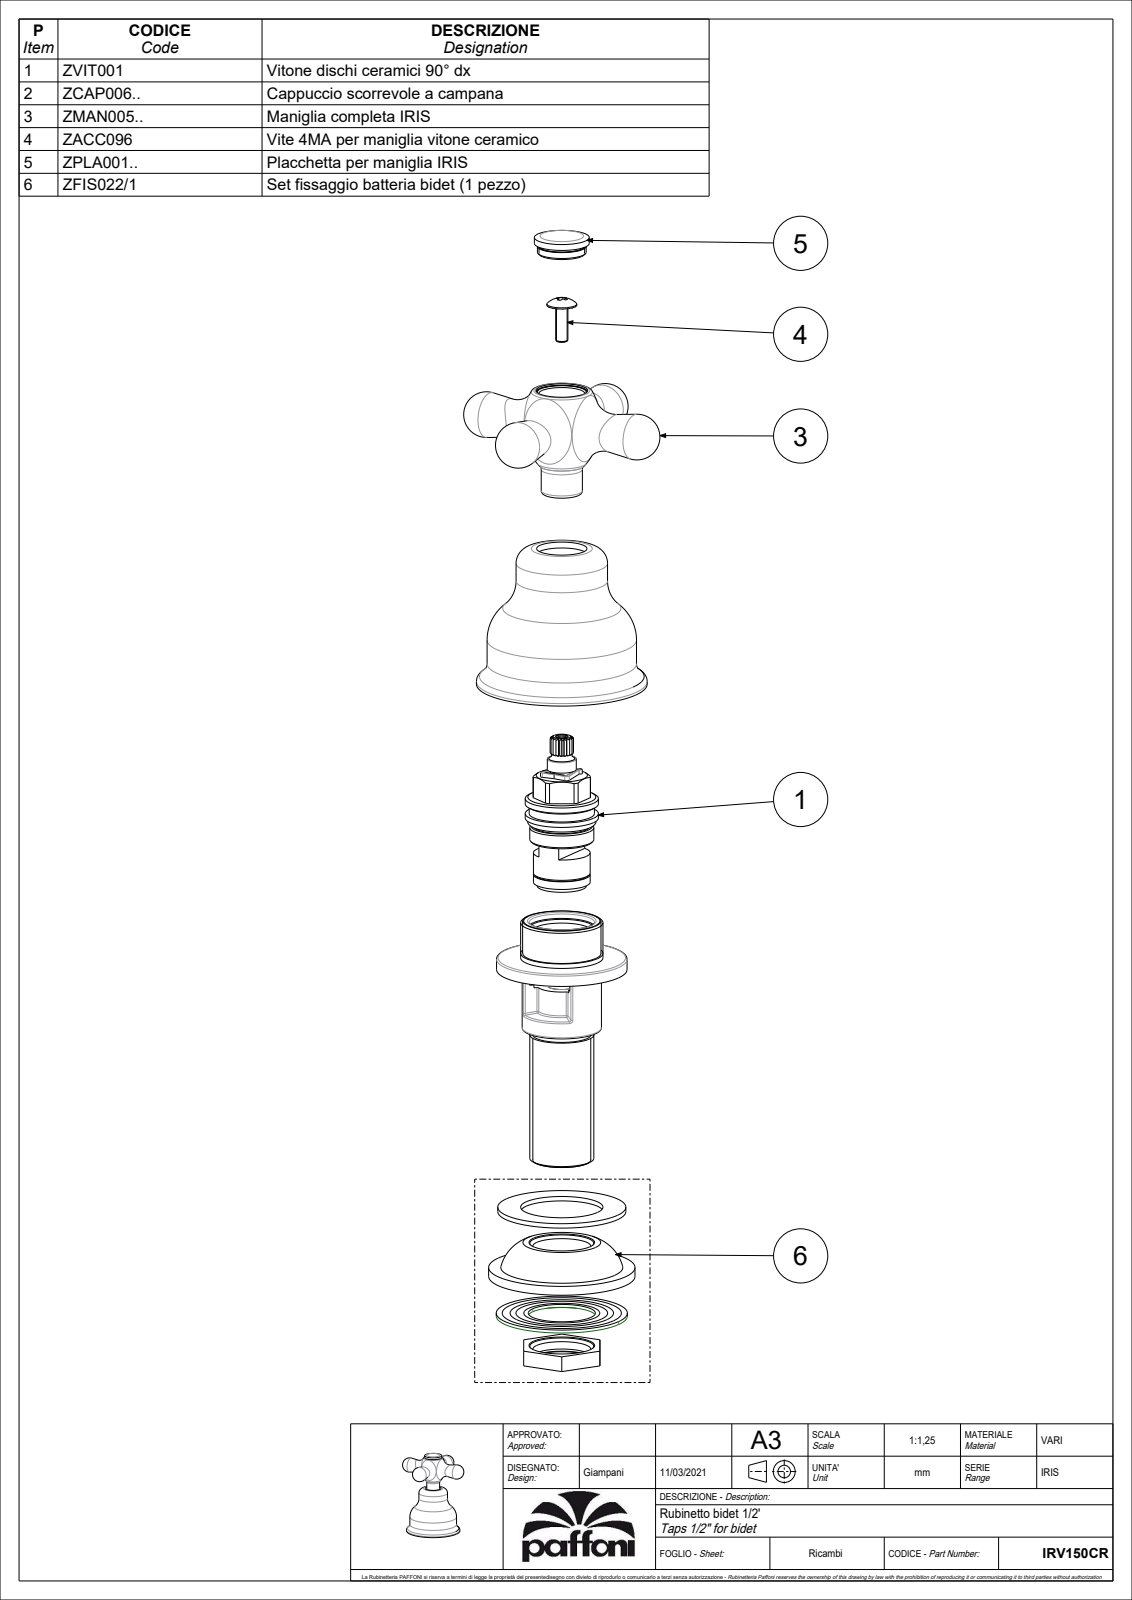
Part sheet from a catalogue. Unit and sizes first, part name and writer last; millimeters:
Units: millimetres
Overall size (bounding box): 83.2 × 72 × 72
Round bosses / shafts (diameter × count): ⌀55 ×1, ⌀49 ×1, ⌀28 ×1, ⌀18 ×1, ⌀13.5 ×1
Main face-to-face distances: 46.5, 79.7, 33.2
Volume: 82 841 mm³ · Surface area: 15 178 mm²
Bodies: 1 solid, 67 faces (3 planar, 10 cylindrical, 54 other)
Part name (STEP PRODUCT): IRV150CR
STEP written by: CREO PARAMETRIC BY PTC INC, 2020044 (CONFIG_CONTROL_DESIGN)
